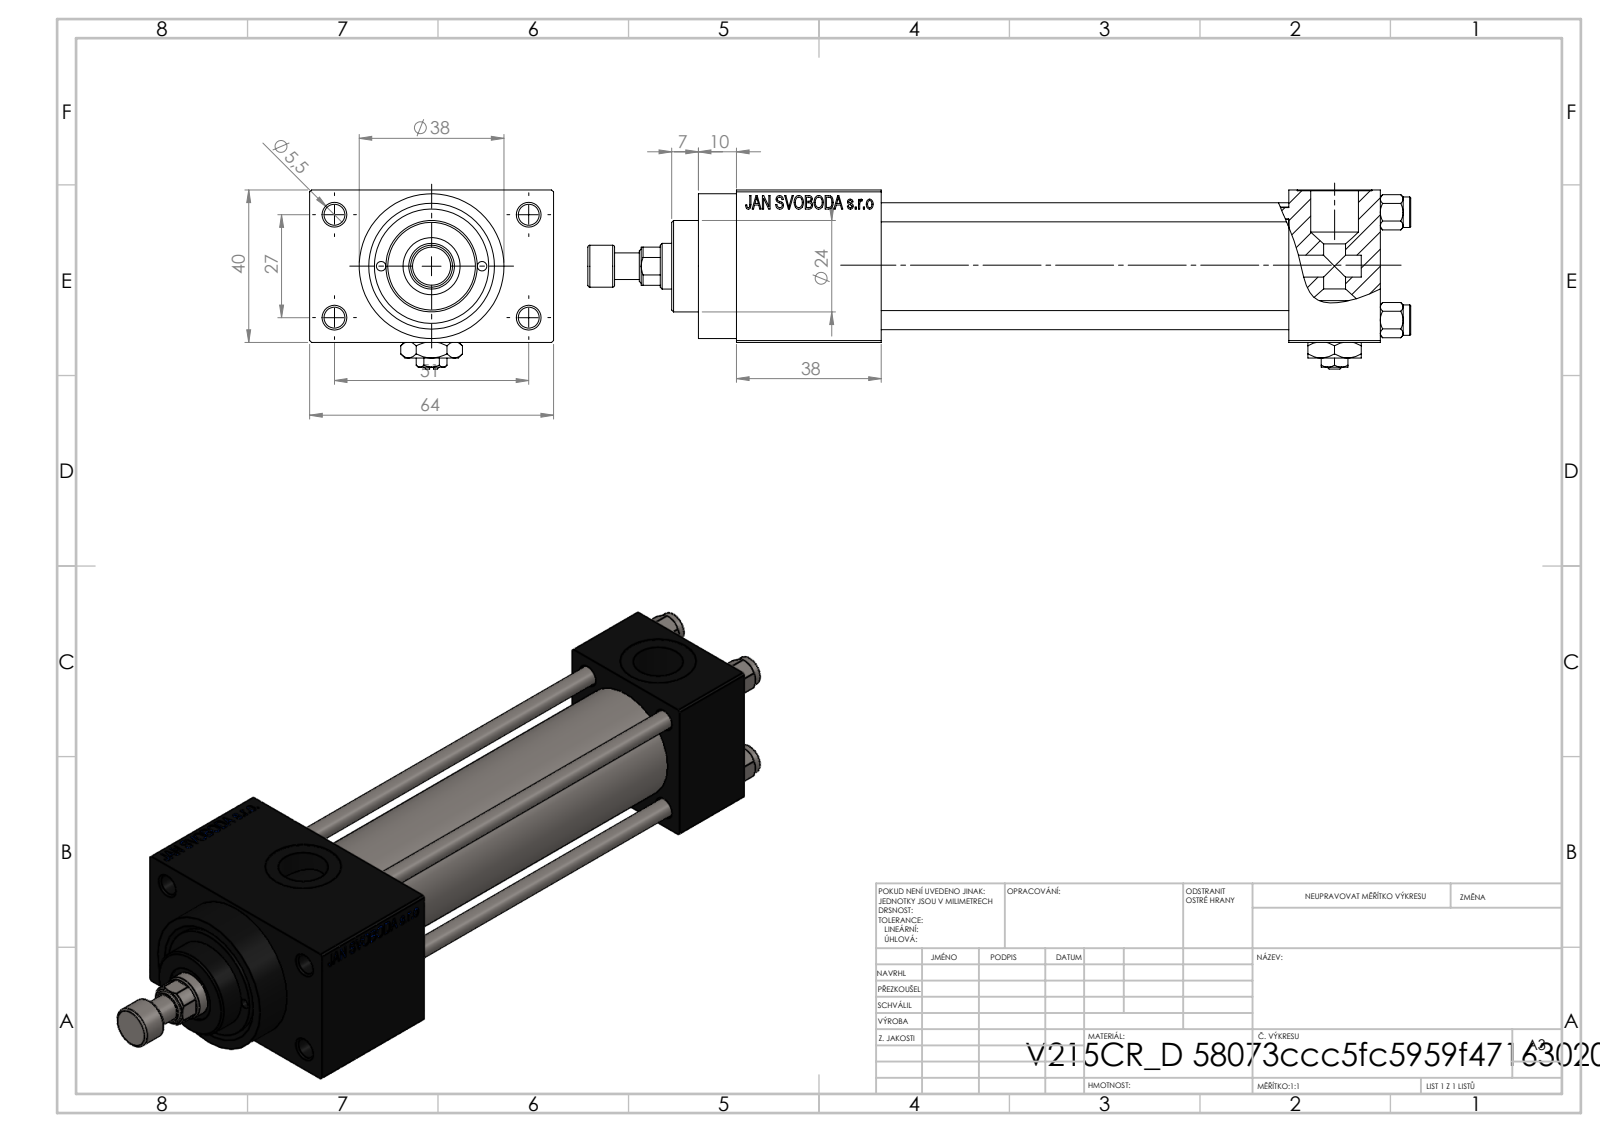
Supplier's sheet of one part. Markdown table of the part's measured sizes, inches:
| quantity | value |
| --- | --- |
| part name | V215CR_D_TYCINKA; V215CR_VCP_D; Zatka_pro_OIL_PORT; V215_VC_A (+3 more) |
| STEP written by | SolidWorks 2019 (CONFIG_CONTROL_DESIGN) |
| units | inches |
| bodies | 13 solids, 1177 faces (525 planar, 104 cylindrical, 548 other) |
| overall size | 8.504 × 2.52 × 1.85 |
| volume | 12.34 in³ |
| surface area | 123.9 in² |
| round holes (diameter × count) | 0.197 × 4, 0.217 × 4, 0.787 × 3, 0.098 × 2, 0.276 × 2, 0.518 × 2, 0.256 × 1, 0.472 × 1, 0.591 × 1, 0.984 × 1, 1.181 × 1 |
| round bosses / shafts (diameter × count) | 0.315 × 4, 1.496 × 1, 1.22 × 1, 0.945 × 1, 0.433 × 1 |
| main face-to-face distances | 1.575, 0.472, 2.047, 4.213, 0.945, 5.157, 2.52, 1.496, 6.654, 5.709 |
| hole center spacings | 0.448, 0.558, 0.718, 0.788, 1.114, 1.136, 1.177, 1.214 |
